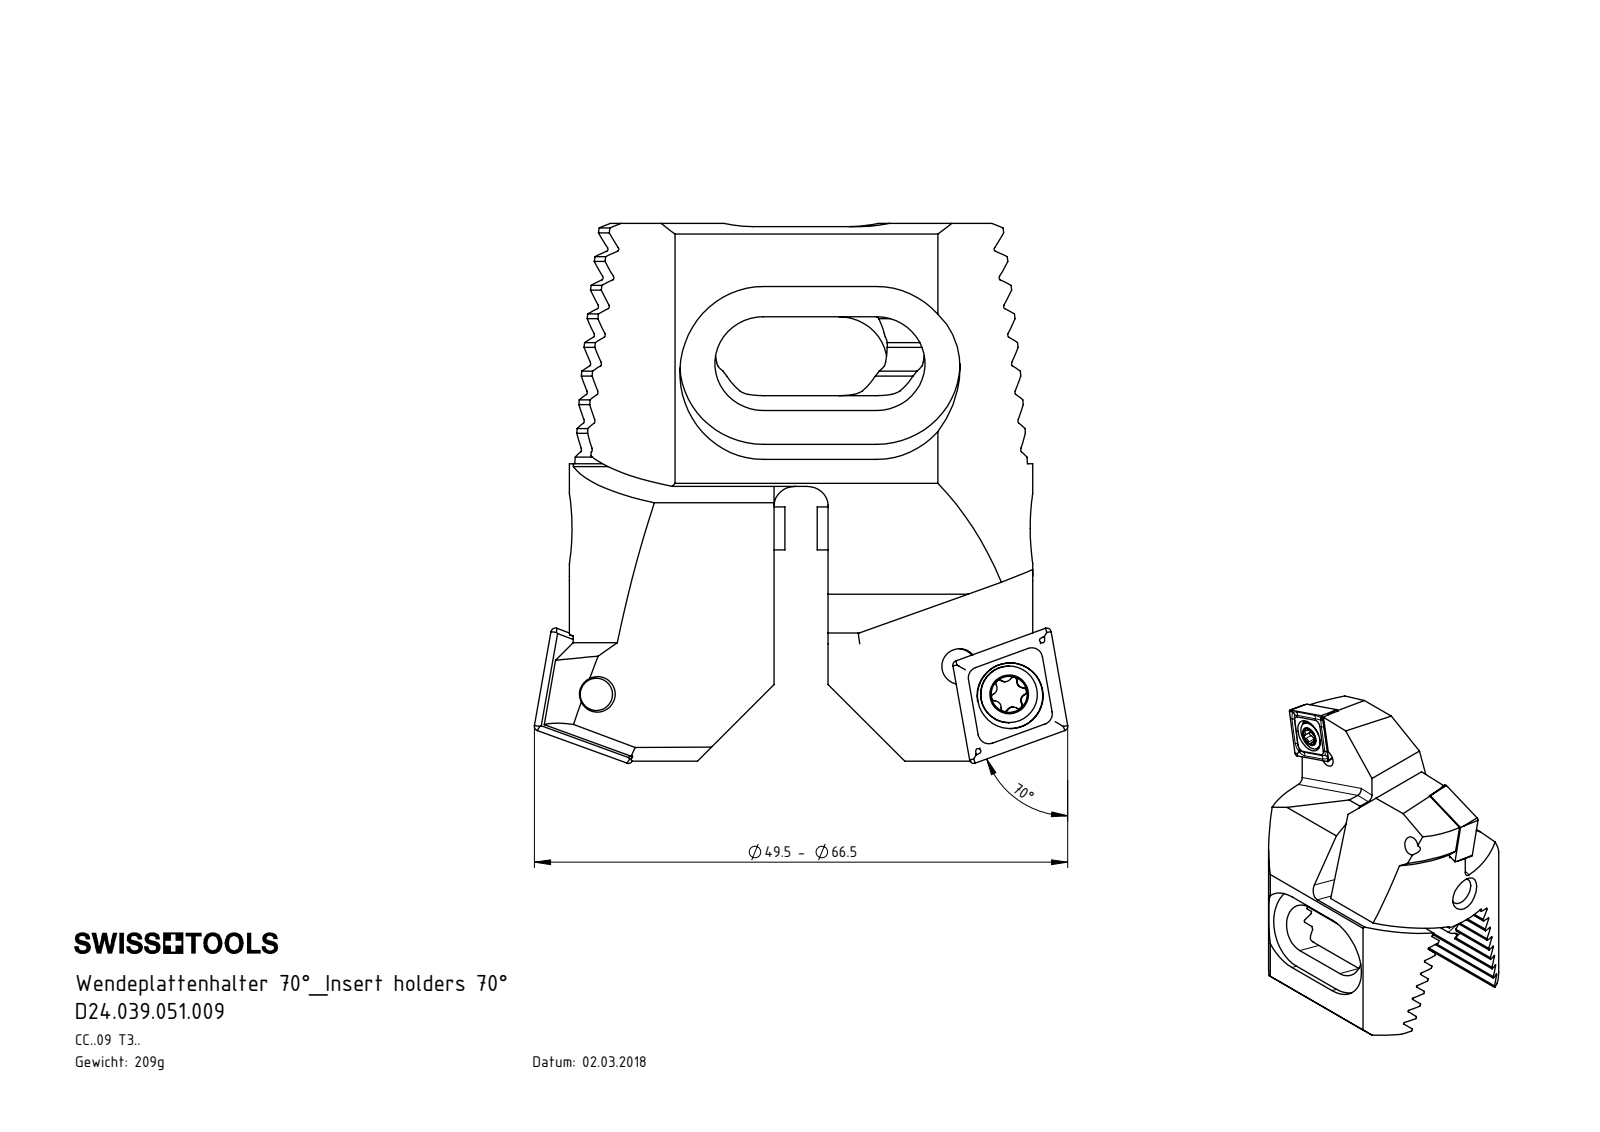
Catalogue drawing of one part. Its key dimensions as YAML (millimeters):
part_name: "D24.039.051.009; CCMT09T304; WCB-ER2.001.009_A; Z42-xxx.001.028_D_70ø (+1 more)"
step_written_by: "SolidWorks 2017 (CONFIG_CONTROL_DESIGN)"
units: millimeters
bodies: {solids: 8, faces: 644, planar: 330, cylindrical: 130, other: 184}
overall_size: [50.1, 49.5, 34.2]
volume: 26611
surface_area: 13423
round_holes:
  - {diameter: 3.3, count: 4}
  - {diameter: 1.6, count: 2}
  - {diameter: 4.4, count: 2}
  - {diameter: 6.1, count: 2}
  - {diameter: 5, count: 1}
round_bosses_or_shafts:
  - {diameter: 4, count: 3}
  - {diameter: 5.25, count: 2}
  - {diameter: 6, count: 1}
partial_cylinders:
  - {radius: 0.2, count: 16}
  - {radius: 0.34, count: 12}
  - {radius: 0.59, count: 12}
  - {radius: 1, count: 4}
  - {radius: 2, count: 4}
  - {radius: 4.5, count: 4}
  - {radius: 7.75, count: 4}
  - {radius: 12, count: 4}
face_to_face_distances: [2.38, 4.76, 11.91, 9.53, 14.29, 7.15, 4.77, 7.14, 1.6, 5.79]
hole_center_spacings: [5.28, 5.43, 12, 34.1, 34.21, 38.7, 23.18, 29.4]
